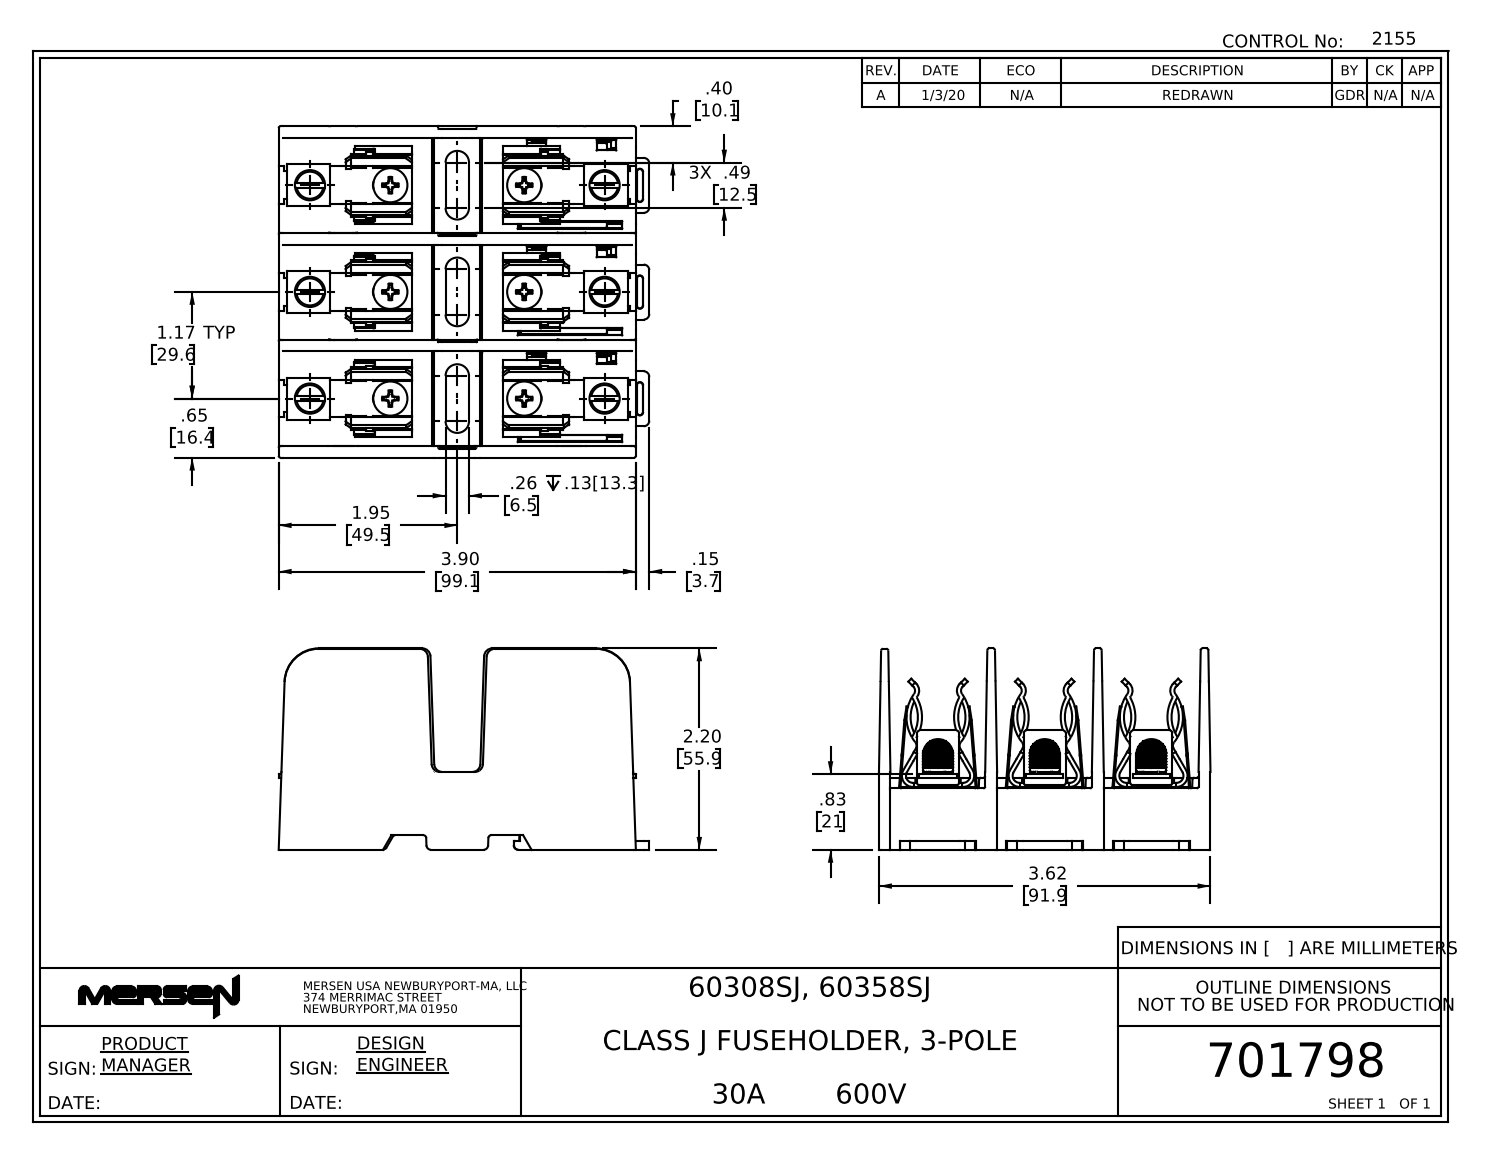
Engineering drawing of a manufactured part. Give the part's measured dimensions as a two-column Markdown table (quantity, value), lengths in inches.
| quantity | value |
| --- | --- |
| part name | 701798revA |
| STEP written by | SolidWorks 2017 (AUTOMOTIVE_DESIGN) |
| units | inches |
| bodies | 37 solids, 3636 faces (1767 planar, 1175 cylindrical, 694 other) |
| overall size | 4.046 × 3.62 × 2.2 |
| volume | 8.022 in³ |
| surface area | 216.4 in² |
| round holes (diameter × count) | 0.156 × 6, 0.33 × 6 |
| round bosses / shafts (diameter × count) | 0.373 × 6, 0.35 × 6, 0.115 × 6, 0.125 × 2, 0.125 × 1 |
| partial cylindrical surfaces (radius × count) | 0.02 × 299, 0.004 × 72, 0.005 × 72, 0.03 × 32, 0.01 × 27, 0.025 × 24, 0.031 × 12, 0.035 × 12 |
| main face-to-face distances | 1.165, 2.33, 0.015, 0.1, 3.495, 0.671, 0.09, 1.065, 0.581, 0.105 |
| hole center spacings | 1.165, 1.459, 2.614, 0.878, 2.34, 1.87, 2.33, 2.49 |
